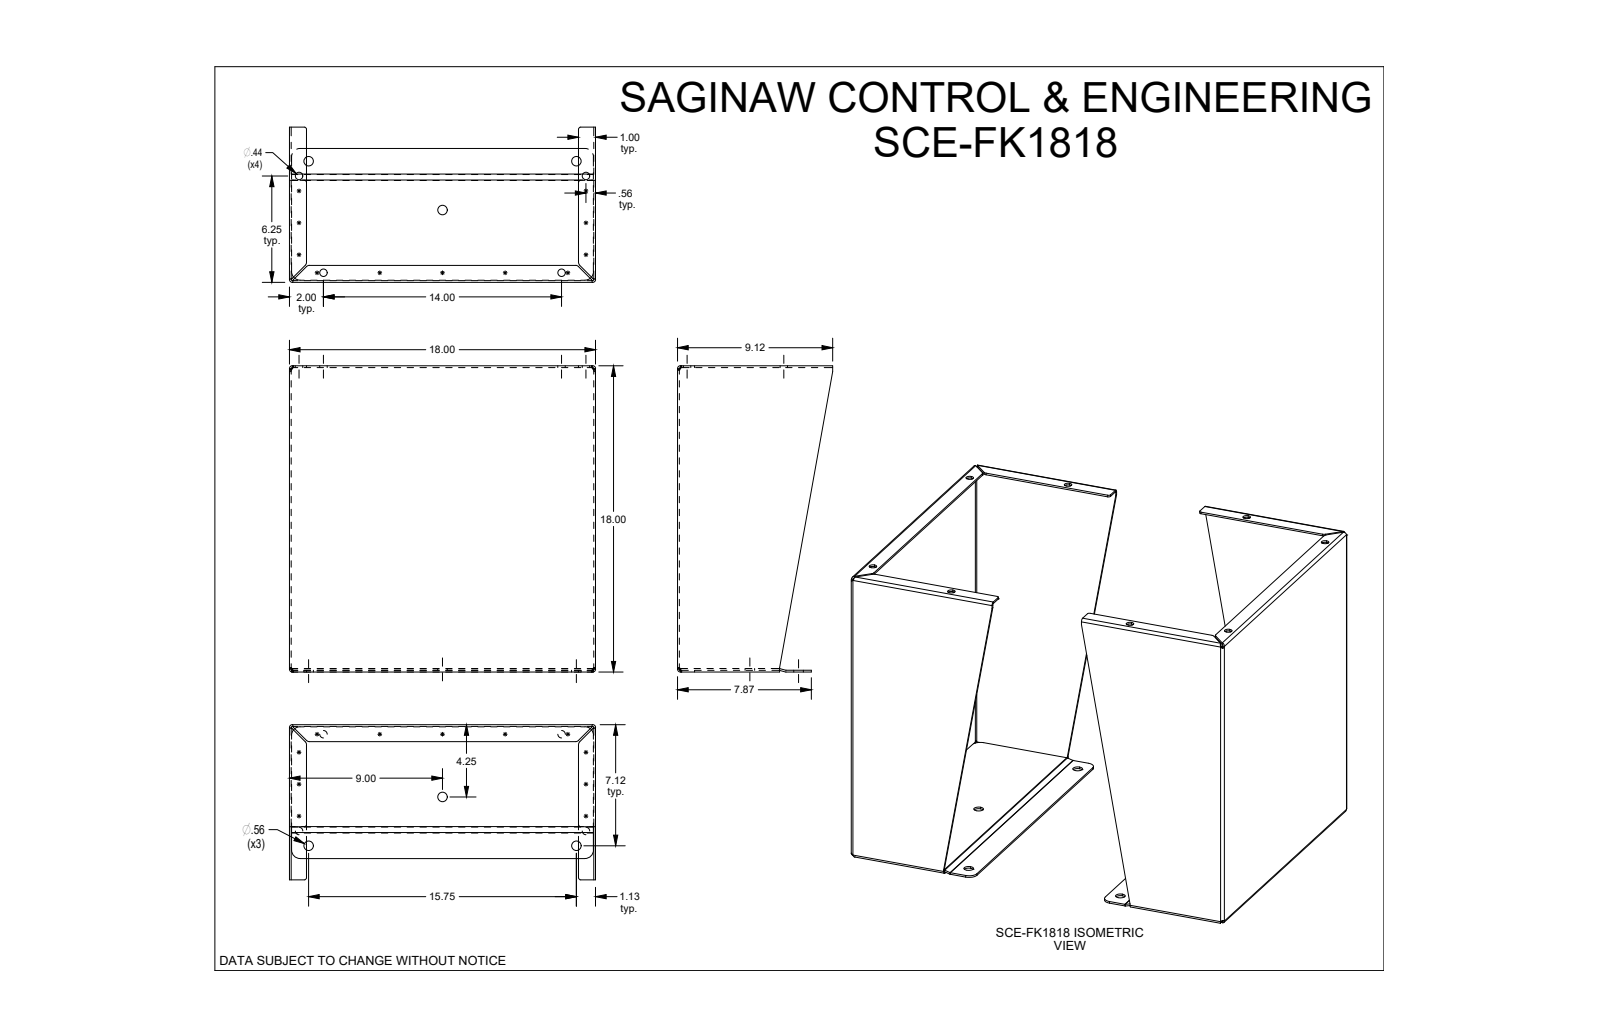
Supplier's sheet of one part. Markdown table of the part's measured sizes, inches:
| quantity | value |
| --- | --- |
| part name | SCE-FK1818 |
| STEP written by | SolidWorks 2019 (CONFIG_CONTROL_DESIGN) |
| units | inches |
| bodies | 4 solids, 214 faces (96 planar, 86 cylindrical, 32 other) |
| overall size | 24 × 18 × 18 |
| volume | 161.9 in³ |
| surface area | 3 150 in² |
| round holes (diameter × count) | 0.437 × 8, 0.563 × 6 |
| partial cylindrical surfaces (radius × count) | 0.166 × 16, 0.062 × 12, 0.125 × 8, 0.22 × 8, 0.5 × 8, 0.063 × 6 |
| main face-to-face distances | 0.104, 23.896, 17.896, 17.792, 24, 23.792, 18, 0.101, 17.893, 17.688 |
| hole center spacings | 1.035, 5.866, 6.614, 7.913, 8.671, 10.646, 14.884, 15.919 |
